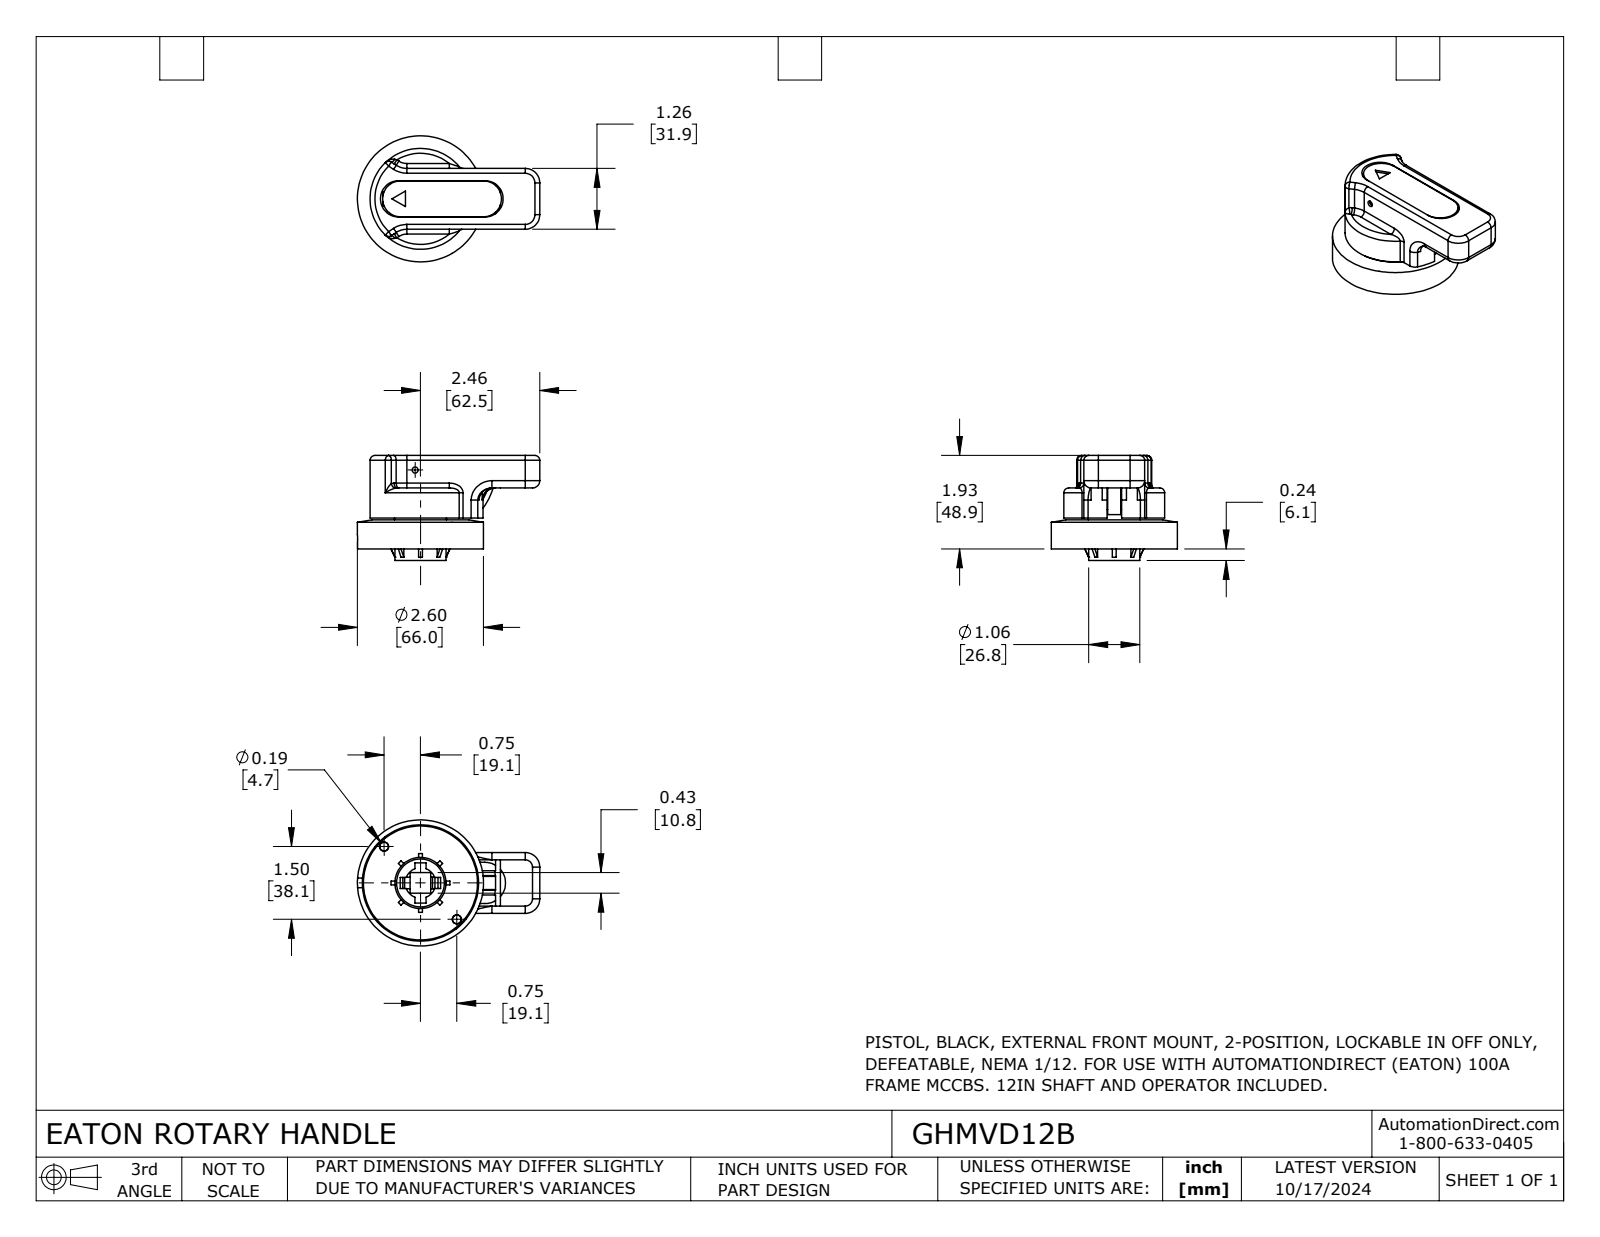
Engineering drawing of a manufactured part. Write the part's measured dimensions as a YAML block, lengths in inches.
part_name: "GHMVD12B"
step_written_by: "SolidWorks 2023 (CONFIG_CONTROL_DESIGN)"
units: inches
bodies: {solids: 5, faces: 334, planar: 181, cylindrical: 114, other: 39}
overall_size: [3.76, 2.6, 2.166]
volume: 3.517
surface_area: 87.63
round_holes:
  - {diameter: 0.18, count: 2}
  - {diameter: 0.187, count: 2}
  - {diameter: 0.125, count: 1}
  - {diameter: 0.175, count: 1}
  - {diameter: 1, count: 1}
  - {diameter: 1.98, count: 1}
  - {diameter: 2.15, count: 1}
  - {diameter: 2.398, count: 1}
round_bosses_or_shafts:
  - {diameter: 2.6, count: 1}
  - {diameter: 2.35, count: 1}
  - {diameter: 1.13, count: 1}
  - {diameter: 1.07, count: 1}
  - {diameter: 1.055, count: 1}
  - {diameter: 0.24, count: 1}
partial_cylinders:
  - {radius: 0.1, count: 14}
  - {radius: 0.15, count: 9}
  - {radius: 0.25, count: 3}
  - {radius: 0.375, count: 3}
  - {radius: 0.3, count: 2}
  - {radius: 0.37, count: 2}
  - {radius: 0.4, count: 2}
  - {radius: 0.425, count: 2}
face_to_face_distances: [0.05, 0.428, 0.778, 0.499, 0.09, 0.409, 0.728, 0.35, 0.378, 0.478]
hole_center_spacings: [1.061, 0.544, 2.121]
